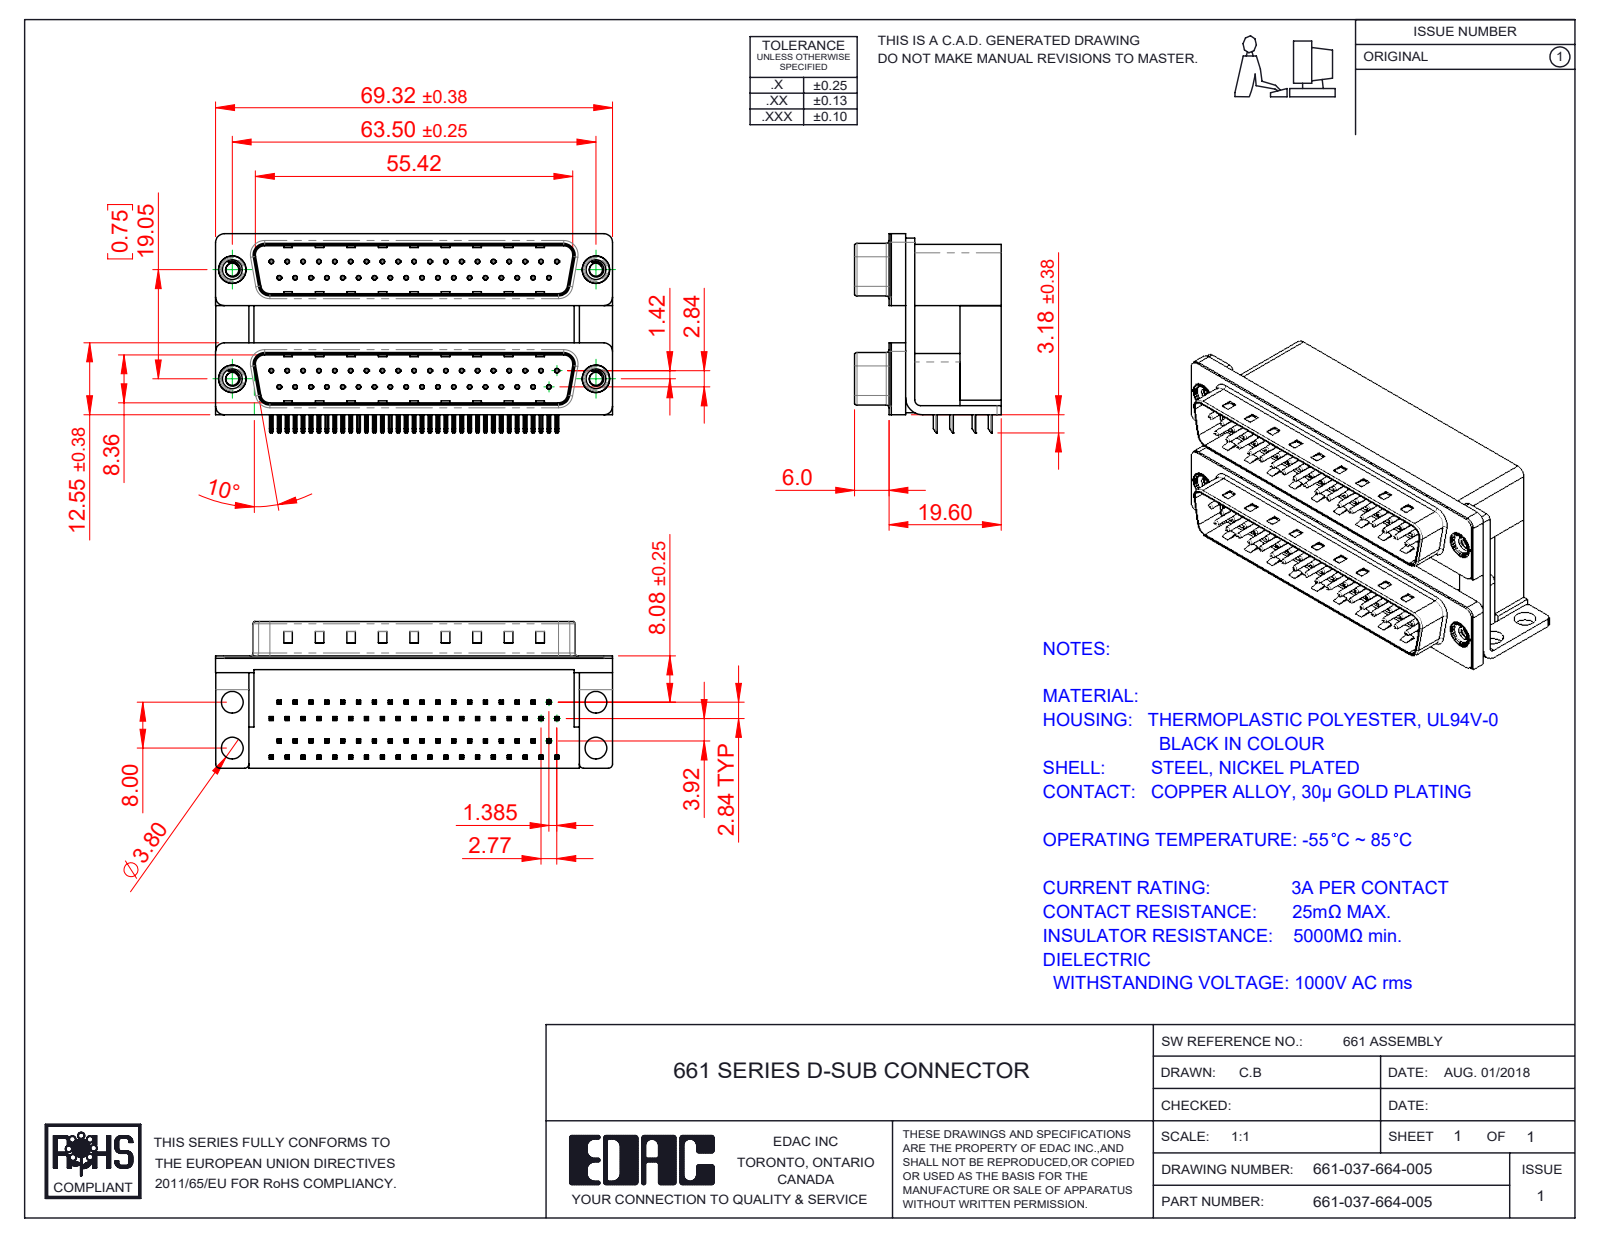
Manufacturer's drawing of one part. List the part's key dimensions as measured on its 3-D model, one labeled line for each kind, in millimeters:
Part name (STEP PRODUCT): 661-037-664-005; 661 Housing Lower_37 Contacts; 661 Mounting Bracket_NoneM; 661 Contact Top Upper_M (+7 more)
STEP written by: SolidWorks 2020 (CONFIG_CONTROL_DESIGN)
Units: millimetres
Bodies: 85 solids, 6582 faces (4250 planar, 1794 cylindrical, 538 other)
Overall size (bounding box): 69.32 × 34.78 × 25.6
Volume: 29 232 mm³ · Surface area: 29 713 mm²
Round holes (diameter × count): ⌀0.35 ×74, ⌀0.8 ×74, ⌀2.26 ×4, ⌀3.5 ×4, ⌀3.8 ×4, ⌀4 ×4, ⌀4.8 ×4, ⌀5 ×4
Round bosses / shafts (diameter × count): ⌀0.75 ×74, ⌀4.9 ×4, ⌀4.75 ×4, ⌀3.9 ×4
Partial cylindrical surfaces — rounded edges, fillets, slot ends (radius × count): R0.25 ×296, R0.12 ×148, R0.5 ×16, R1.5 ×14, R0.75 ×8, R0.9 ×8, R1.6 ×8, R2 ×8
Main face-to-face distances: 19.05, 0.4, 19.2, 10.69, 7.2, 12, 8.36, 8.76, 18.7, 2.84
Hole centre spacings: 2.77, 5.54, 3.16, 8.31, 11.08, 13.85, 16.62, 19.39
